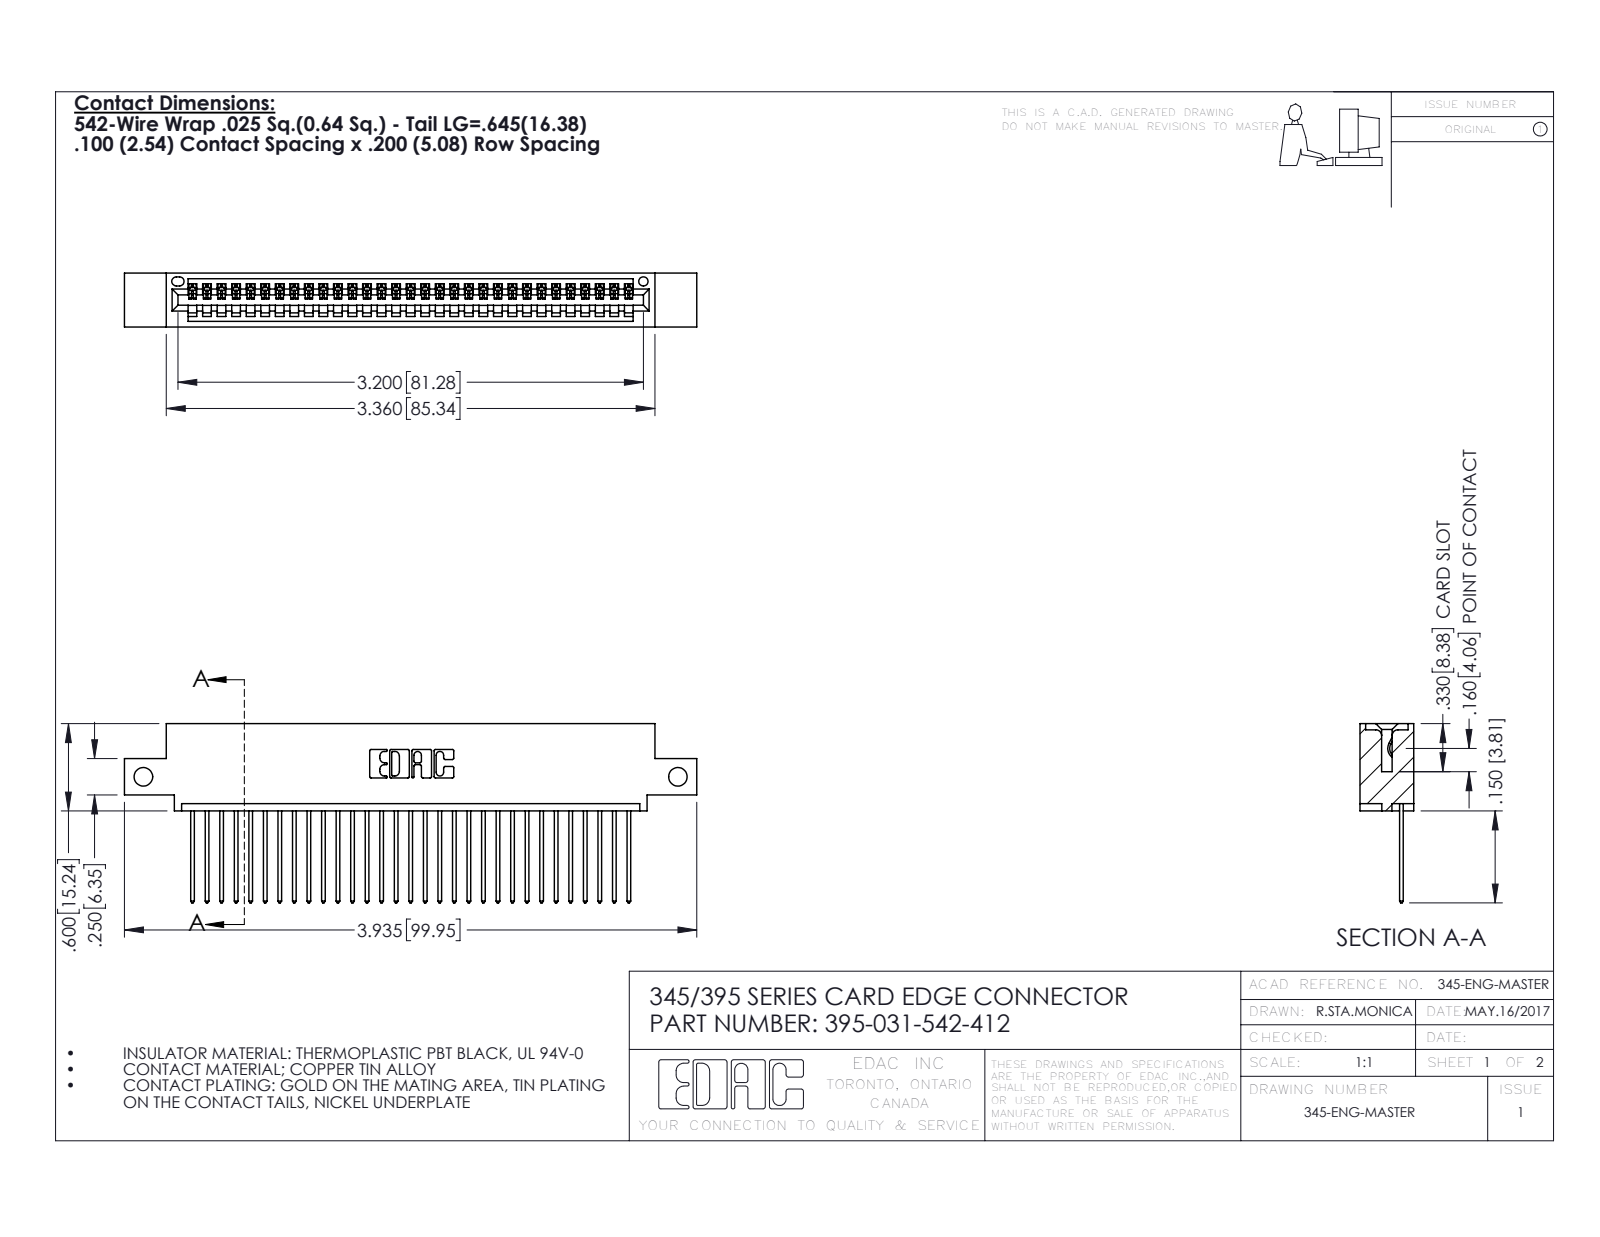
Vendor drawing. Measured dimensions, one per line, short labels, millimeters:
name: 345 Part_0.110 Offset - Side Mount; 345-292-001_345-293-142; 395-031-542-412
written by: SolidWorks 2016 (CONFIG_CONTROL_DESIGN)
unit: mm
bodies: 32 solids, 1928 faces (1324 planar, 604 cylindrical, 0 other)
size: 99.9 × 31.3 × 9.4
volume: 9 310 mm³; area: 12 600 mm²
holes: 2× ⌀3.3, 1× ⌀1.6
rounds: 62× R0.2, 62× R0.3, 22× R0.3, 6× R0.2, 6× R0.8, 3× R0.7, 2× R0.8, 2× R1
face distances: 7.6, 1.8, 9.4, 5.1, 2.5, 6.9, 0.6, 5.7, 3.8, 1.8
hole spacings: 93.3
